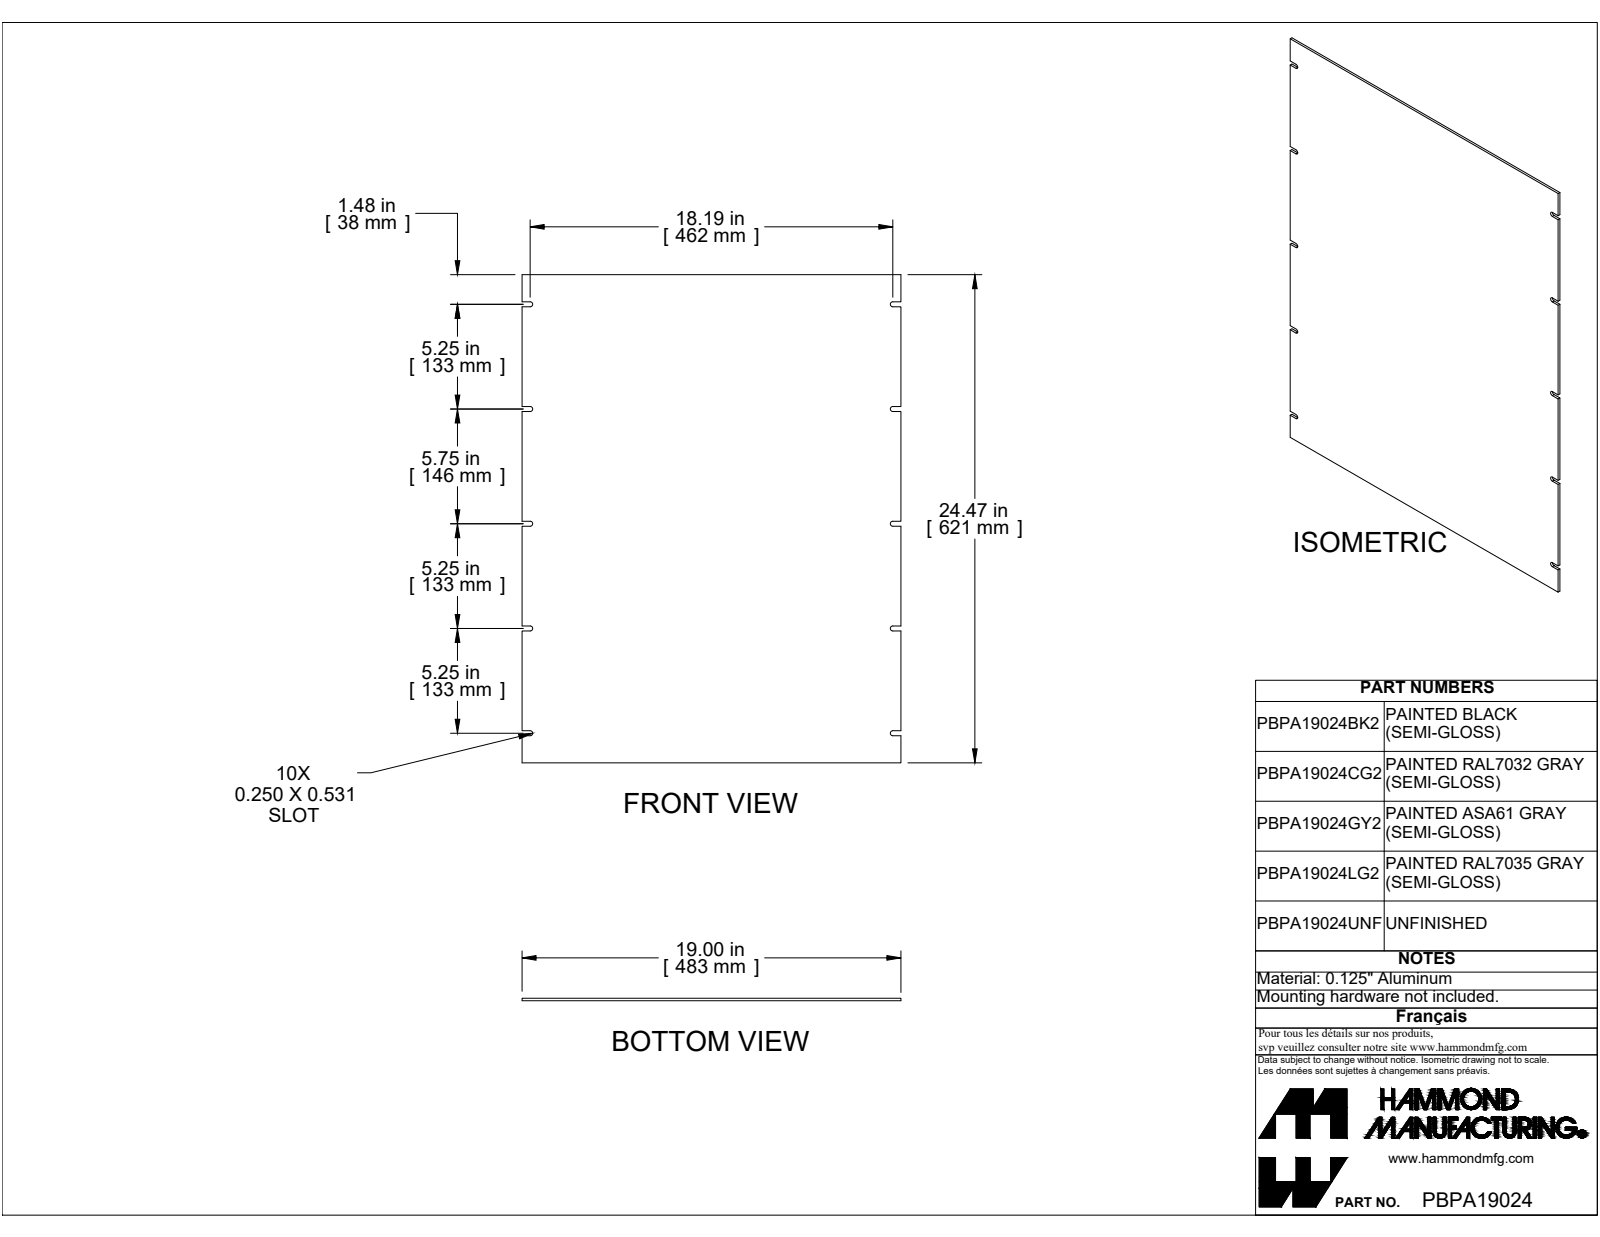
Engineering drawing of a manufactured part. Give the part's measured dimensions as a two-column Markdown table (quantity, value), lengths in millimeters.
| quantity | value |
| --- | --- |
| part name | PBPA19024UNF |
| STEP written by | SolidWorks 2019 (CONFIG_CONTROL_DESIGN) |
| units | millimeters |
| bodies | 1 solid, 46 faces (36 planar, 10 cylindrical, 0 other) |
| overall size | 621.5 × 482.6 × 3.2 |
| volume | 949 600 mm³ |
| surface area | 606 000 mm² |
| partial cylindrical surfaces (radius × count) | 3.2 × 10 |
| main face-to-face distances | 3.2, 482.6, 621.5, 133.4, 412.8, 6.4, 139.7, 127, 279.4, 34.5 |
